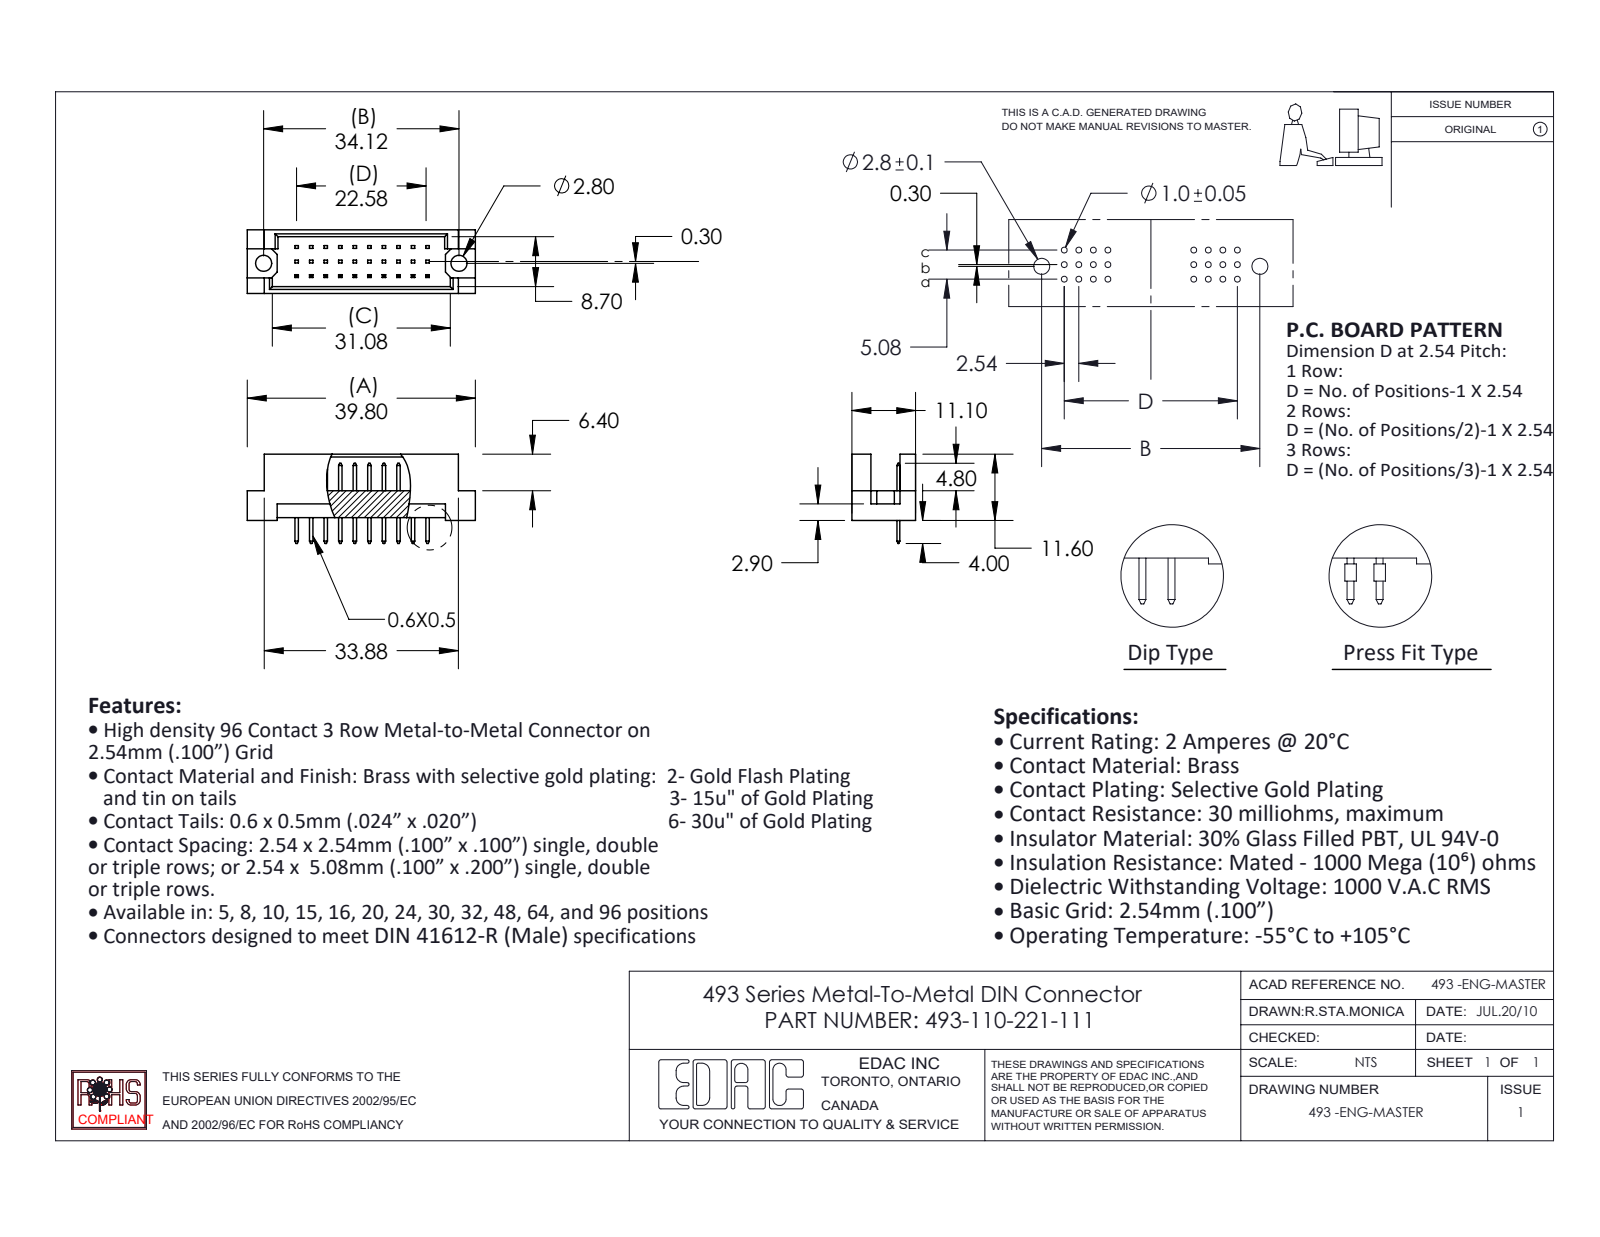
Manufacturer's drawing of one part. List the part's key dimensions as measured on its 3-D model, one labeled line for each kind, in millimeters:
Part name (STEP PRODUCT): 493-110-221-112; 493 Part_30; 493-290_21
STEP written by: SolidWorks 2020 (CONFIG_CONTROL_DESIGN)
Units: millimetres
Bodies: 11 solids, 312 faces (308 planar, 4 cylindrical, 0 other)
Overall size (bounding box): 39.8 × 15.6 × 11.1
Volume: 2 414 mm³ · Surface area: 3 042 mm²
Round holes (diameter × count): ⌀2.8 ×2
Main face-to-face distances: 1.2, 9.9, 11.1, 8.7, 2.54, 0.5, 4.7, 5.08, 2.76, 3.26
Hole centre spacings: 34.12
